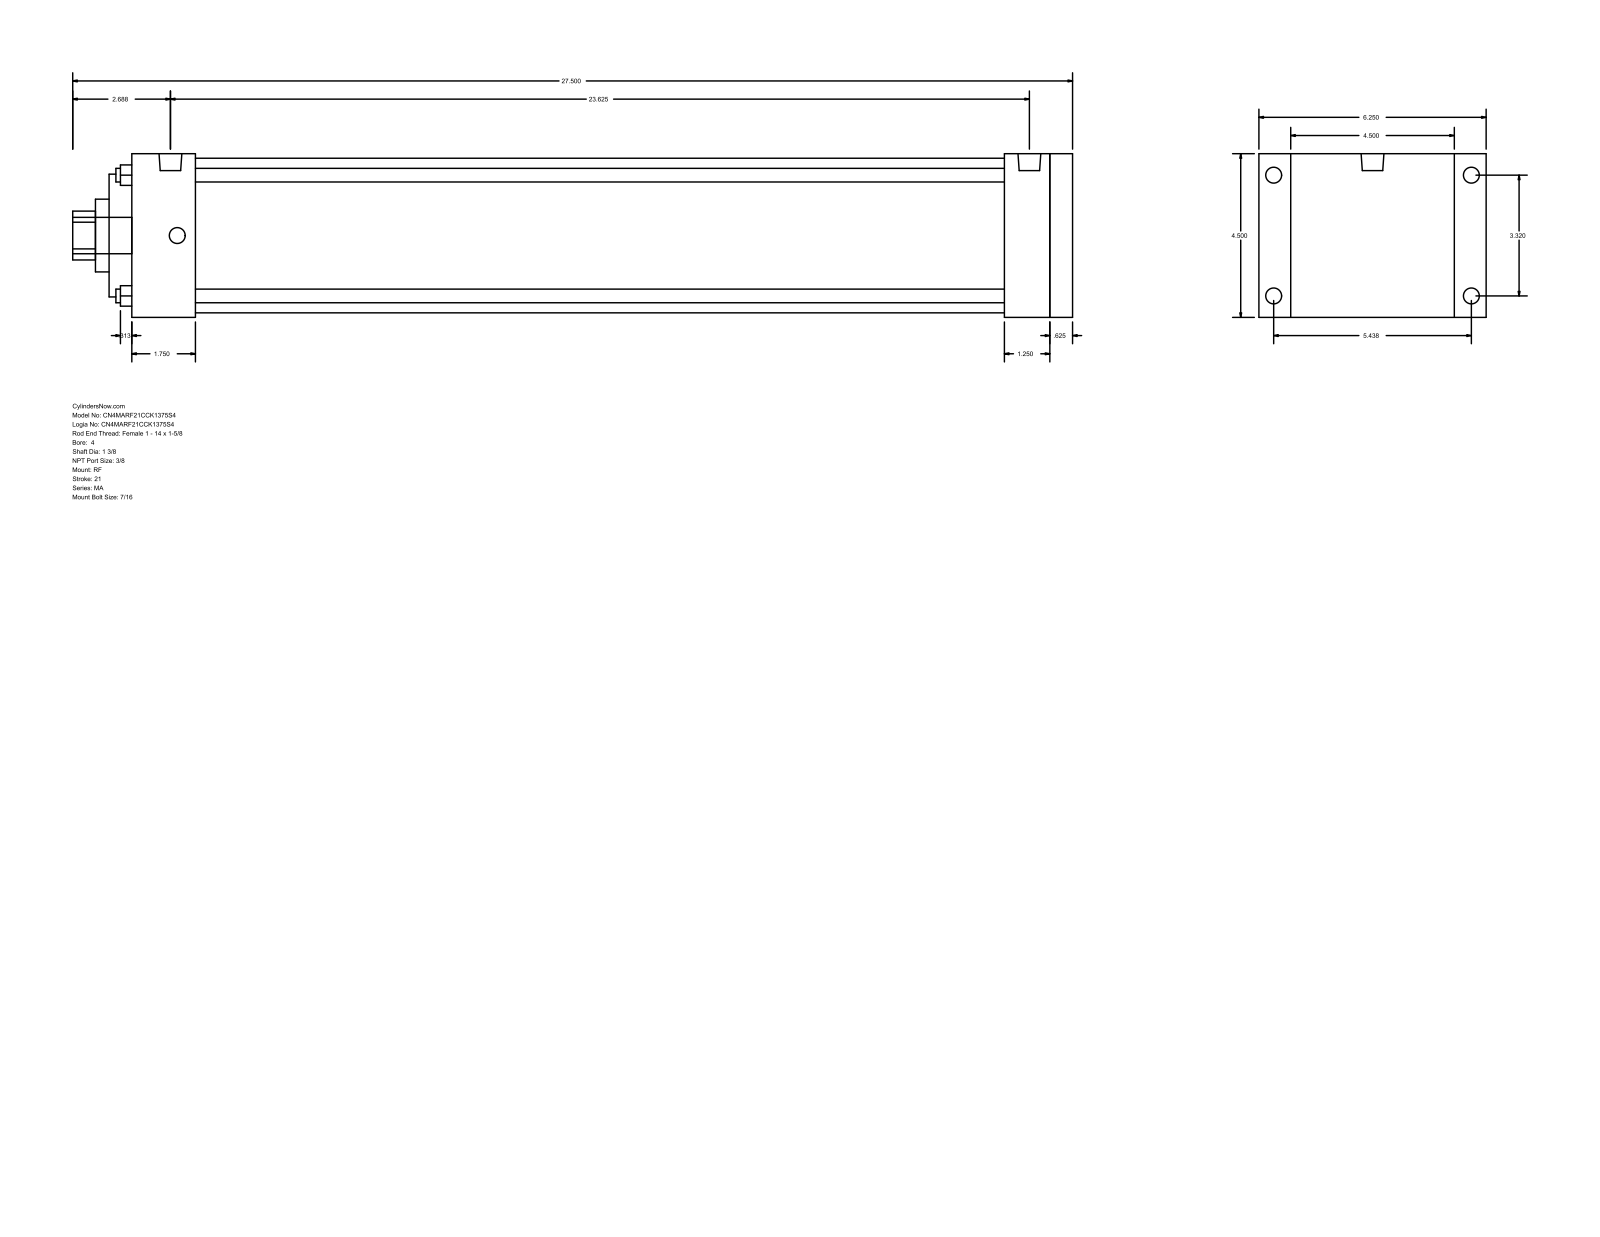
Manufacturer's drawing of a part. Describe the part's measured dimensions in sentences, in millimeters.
The part is named "MA_RF__0400_1.375". Its 3-D file was written by "GSSL Pune (CONFIG_CONTROL_DESIGN)". It is 0 solids with 94 faces: 65 planar, 29 cylindrical and 0 other. Overall it measures 698.5 by 158.75 by 114.3 millimeters. Round holes: 4 of diameter 9.53, 1 of diameter 34.92, 1 of diameter 50.8, 1 of diameter 85.72, 1 of diameter 107.95. Round bosses or shafts: 8 of diameter 11.11, 2 of diameter 15.93, 1 of diameter 25.4. Partial cylindrical surfaces (rounded edges, fillets, slot ends): 1 of radius 17.06. The main face-to-face distances are 114.3, 657.23, 15.88, 641.35, 15.87, 657.22, 673.1, 22.23, 136.53, 625.48. The hole center spacings are 59.62, 84.32, 119.25.
